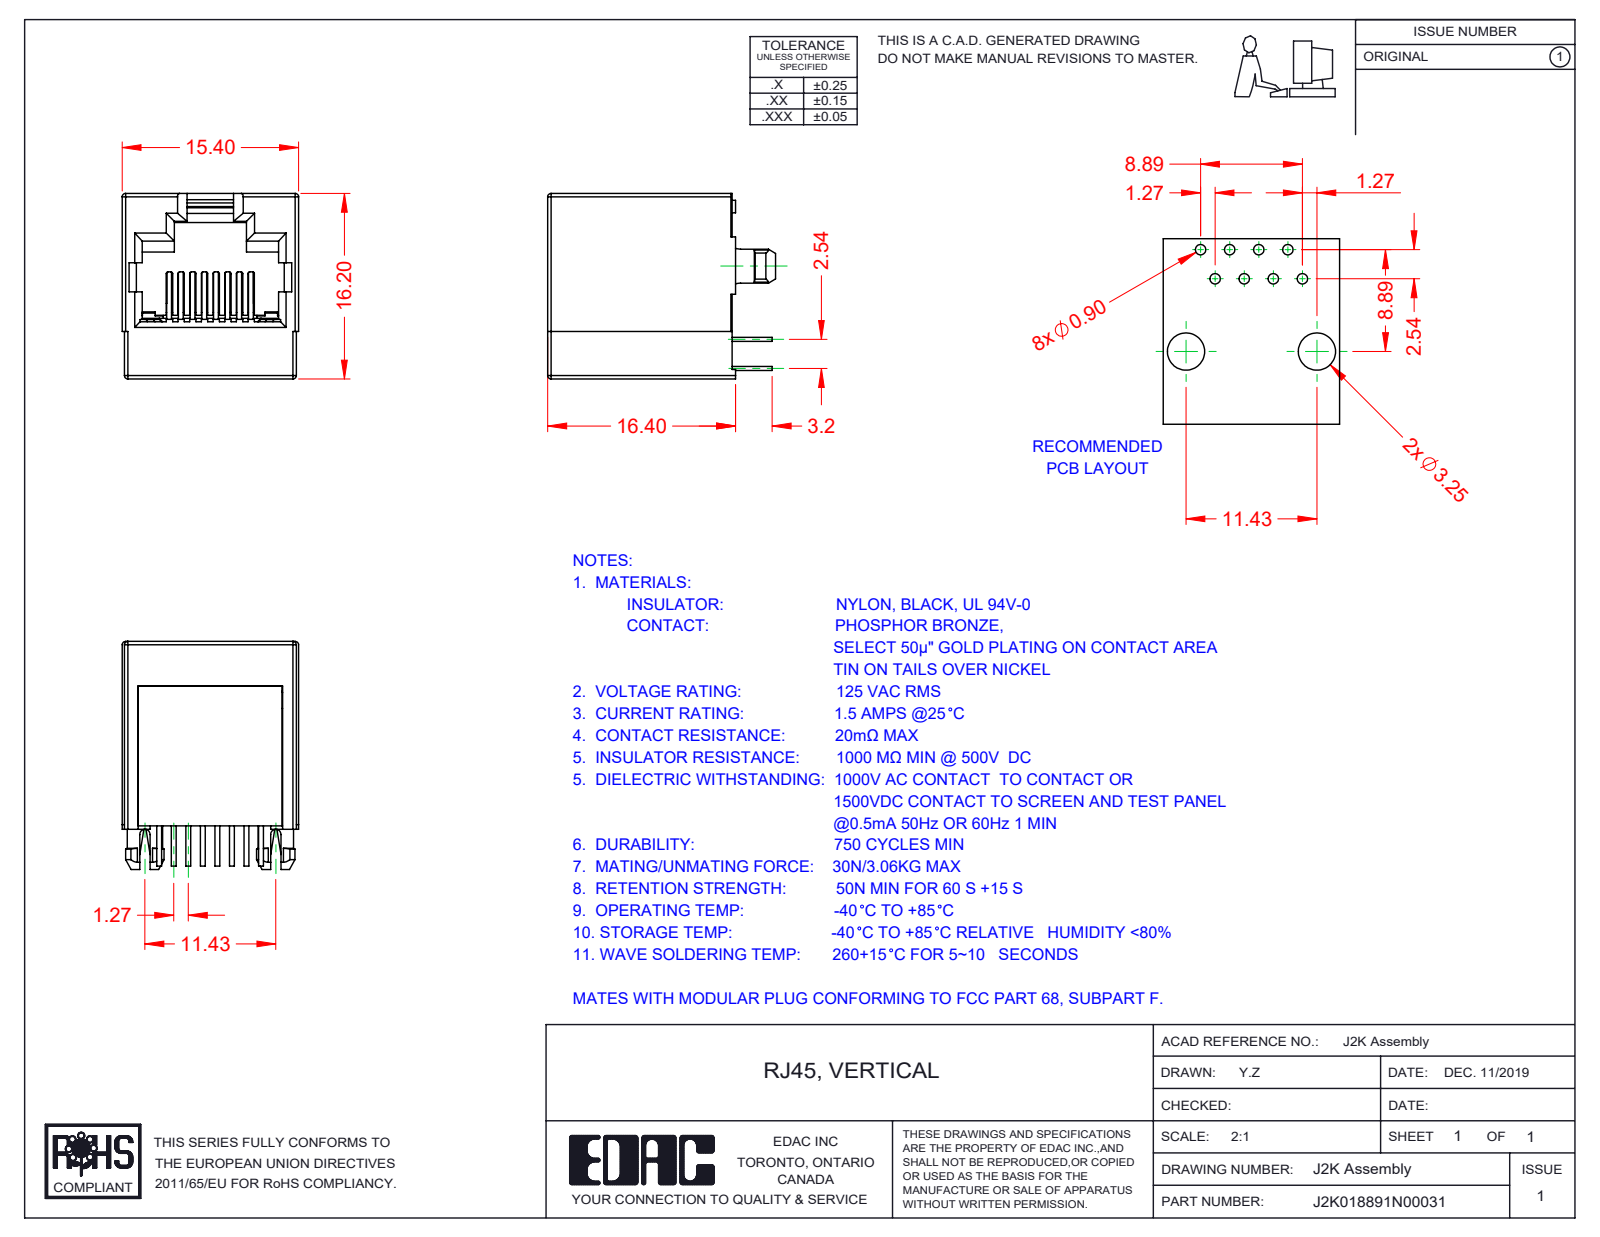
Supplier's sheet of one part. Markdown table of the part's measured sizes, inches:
| quantity | value |
| --- | --- |
| part name | 2K Contacts; 2K Insulator; 2K Contact Lock; RJ2K018891N00031 |
| STEP written by | SolidWorks 2016 (CONFIG_CONTROL_DESIGN) |
| units | inches |
| bodies | 10 solids, 723 faces (586 planar, 113 cylindrical, 24 other) |
| overall size | 0.783 × 0.638 × 0.606 |
| volume | 0.151 in³ |
| surface area | 6.141 in² |
| round bosses / shafts (diameter × count) | 0.122 × 2, 0.043 × 2 |
| partial cylindrical surfaces (radius × count) | 0.006 × 16, 0.012 × 10, 0.02 × 3, 0.004 × 2, 0.008 × 2, 0.018 × 2, 0.024 × 2, 0.037 × 2 |
| main face-to-face distances | 0.638, 0.606, 0.055, 0.551, 0.047, 0.543, 0.598, 0.014, 0.02, 0.591 |
